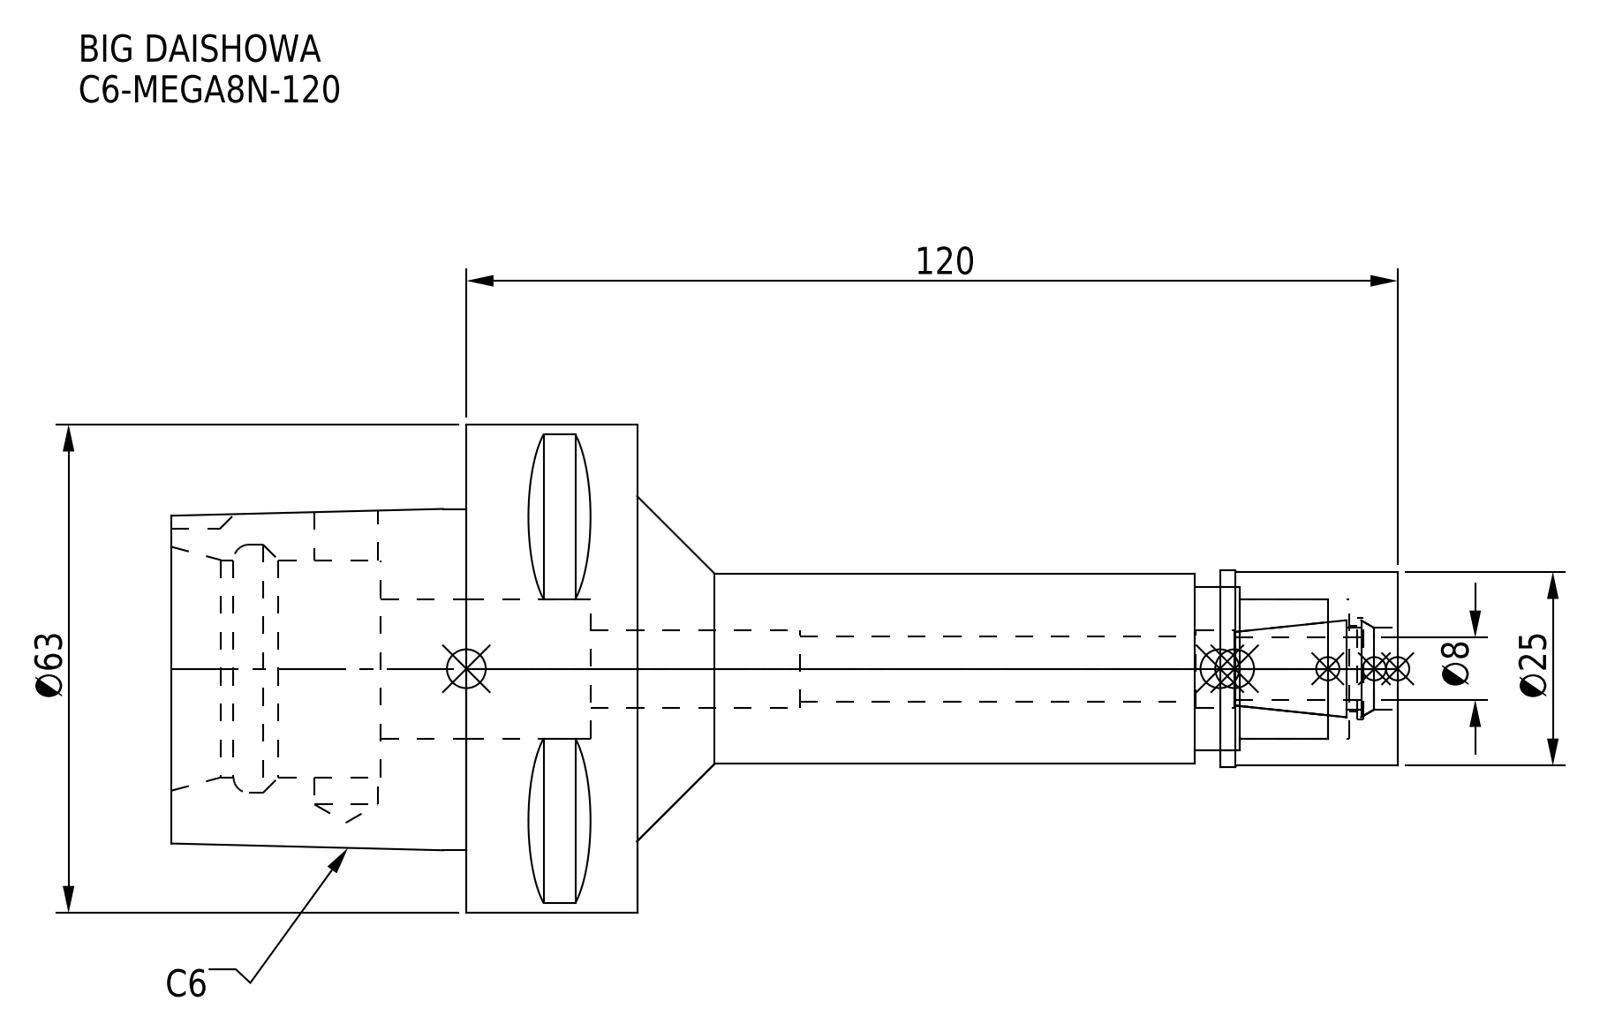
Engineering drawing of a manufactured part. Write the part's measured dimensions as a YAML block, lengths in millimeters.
part_name: "DXF_TEMP_ASSY_ASM_4_ASM.stp; MGN8_1.stp; C6-MEGA8N-120; C6-MEGA8N-120-080_ASM.stp (+3 more)"
step_written_by: "SolidWorks 2019 (CONFIG_CONTROL_DESIGN)"
units: millimeters
bodies: {solids: 2, faces: 98, planar: 39, cylindrical: 41, other: 18}
overall_size: [158, 63, 63]
volume: 139991
surface_area: 32859
round_holes:
  - {diameter: 8.1, count: 1}
  - {diameter: 8.4, count: 1}
  - {diameter: 10, count: 1}
  - {diameter: 10.5, count: 1}
  - {diameter: 11, count: 1}
  - {diameter: 13, count: 1}
  - {diameter: 18, count: 1}
  - {diameter: 21, count: 1}
  - {diameter: 28, count: 1}
  - {diameter: 32, count: 1}
round_bosses_or_shafts:
  - {diameter: 63, count: 1}
  - {diameter: 25.3, count: 1}
  - {diameter: 25, count: 1}
  - {diameter: 24.5, count: 1}
partial_cylinders:
  - {radius: 5, count: 1}
face_to_face_distances: [22, 27, 60, 38, 98, 120, 158, 131, 33, 11]
